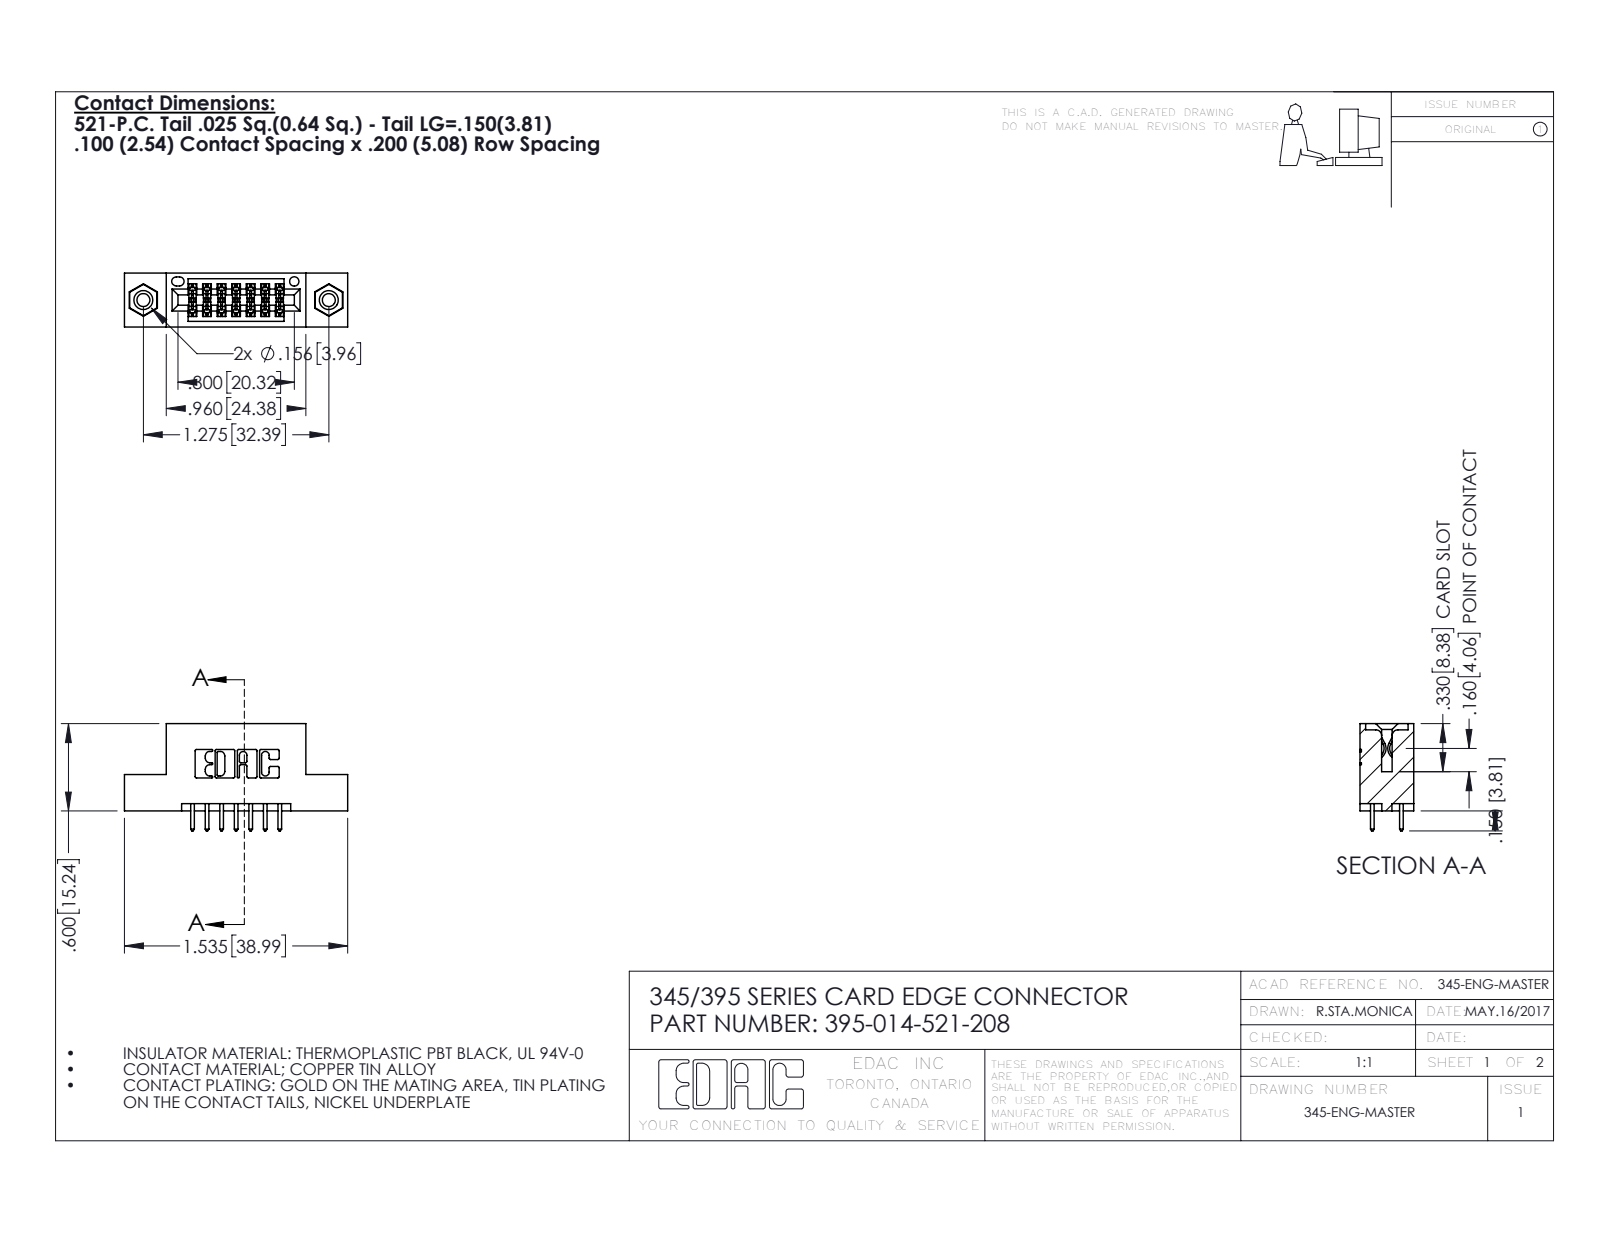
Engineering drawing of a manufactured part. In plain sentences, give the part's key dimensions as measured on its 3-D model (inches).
The part is named "345-250-001_345-250-003-102; 345 Part_Flush Mounting Lugs - 0.156 Dia-TI; 395-014-521-208; 345-292-001_345-293-121". Its 3-D file was written by "SolidWorks 2016 (CONFIG_CONTROL_DESIGN)". It is 17 solids with 886 faces: 574 planar, 296 cylindrical and 16 other. Overall it measures 1.535 by 0.737 by 0.37 inches. Its volume is 0.211 cubic inches and its surface area 6.818 square inches. Round holes: 2 of diameter 0.089, 2 of diameter 0.125, 2 of diameter 0.156, 1 of diameter 0.064. Round bosses or shafts: 2 of diameter 0.155. Partial cylindrical surfaces (rounded edges, fillets, slot ends): 22 of radius 0.01, 21 of radius 0.006, 14 of radius 0.01, 6 of radius 0.007, 6 of radius 0.031, 3 of radius 0.026, 2 of radius 0.014, 2 of radius 0.019. The main face-to-face distances are 0.2, 0.072, 0.298, 0.37, 0.1, 0.098, 0.272, 0.025, 0.3, 0.225. The hole center spacings are 0.27, 1.045, 1.275.
